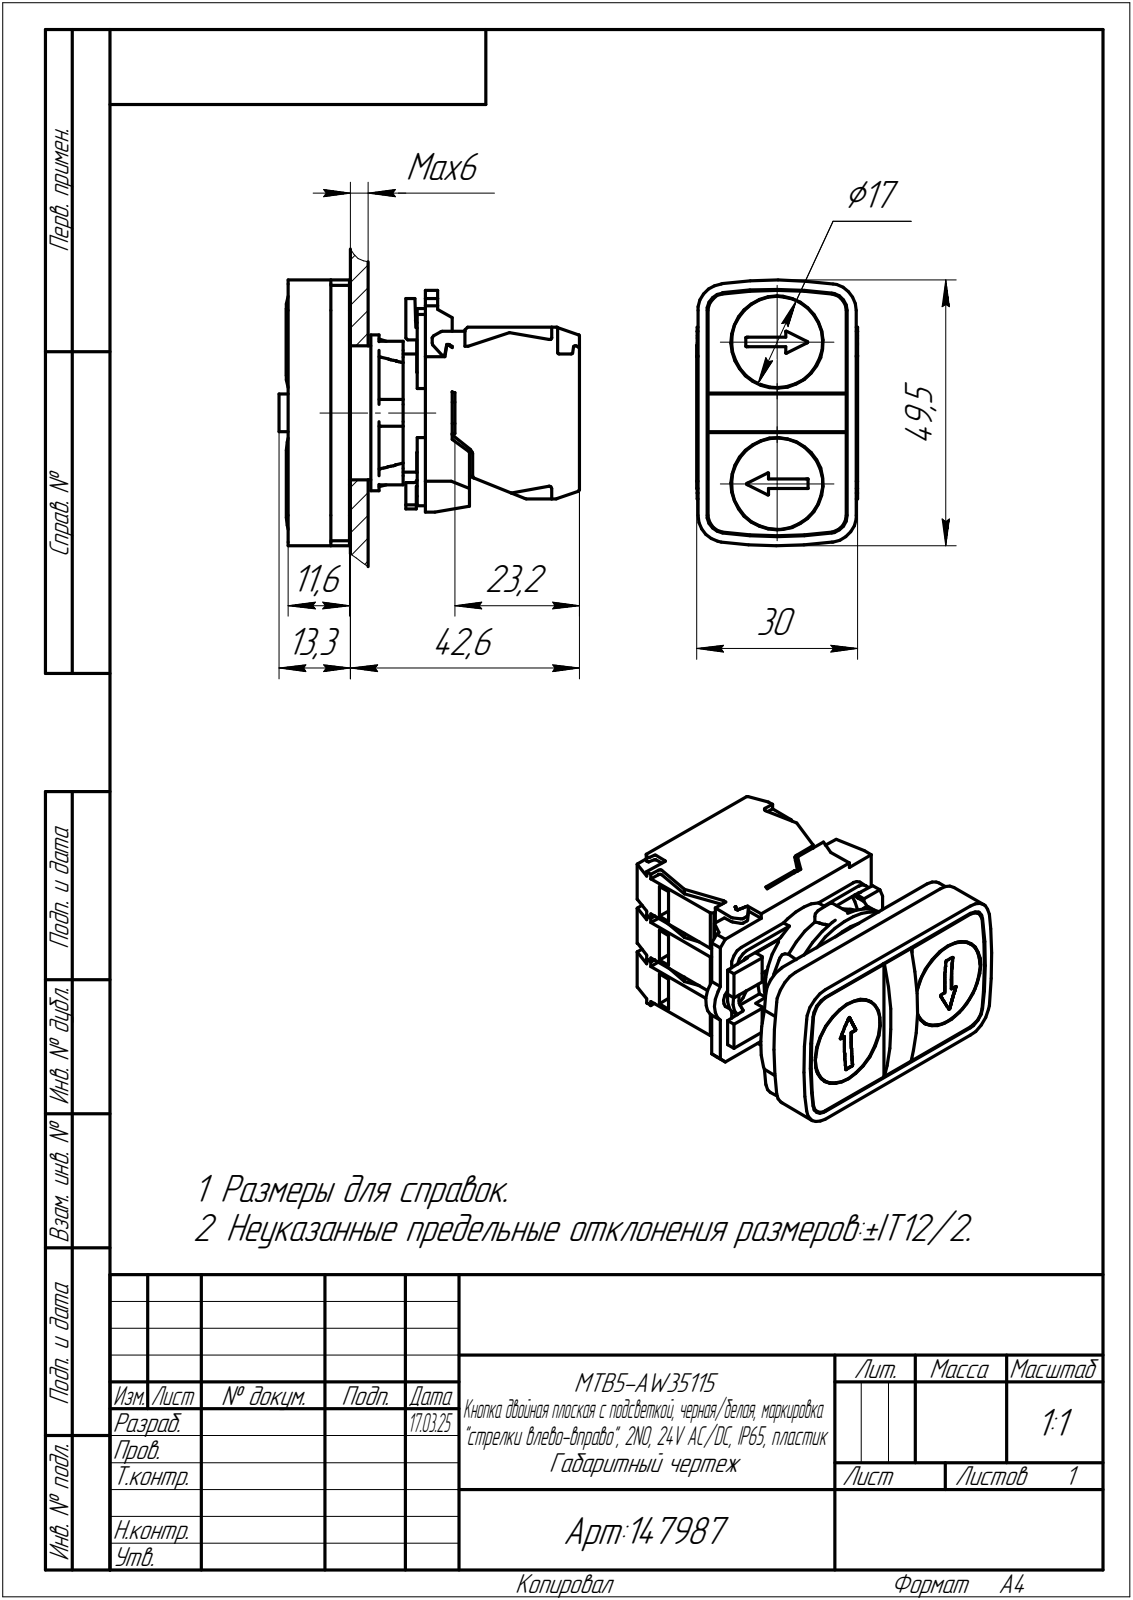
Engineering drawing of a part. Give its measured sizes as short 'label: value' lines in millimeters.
name: LA167-B5-AWA3512315-24V
written by: PRO/ENGINEER BY PARAMETRIC TECHNOLOGY CORPORATION, 2010280 (CONFIG_CONTROL_DESIGN)
unit: mm
bodies: 1 solid, 676 faces (451 planar, 200 cylindrical, 25 other)
size: 55.9 × 49.5 × 30
volume: 47 740 mm³; area: 19 405 mm²
holes: 2× ⌀6, 2× ⌀17.2, 1× ⌀5.2, 1× ⌀20.5
bosses: 2× ⌀17, 1× ⌀29, 1× ⌀26.8, 1× ⌀25, 1× ⌀22
rounds: 15× R1, 13× R0.2, 10× R0.1, 7× R0.5, 4× R2.5, 4× R3.1, 4× R3.3, 4× R4.35
face distances: 10, 9.9, 20, 19.9, 10.1, 14.1, 9, 25.5, 11.4, 19.1
hole spacings: 4.7, 8.5, 13.2, 21.7, 17, 26.4
